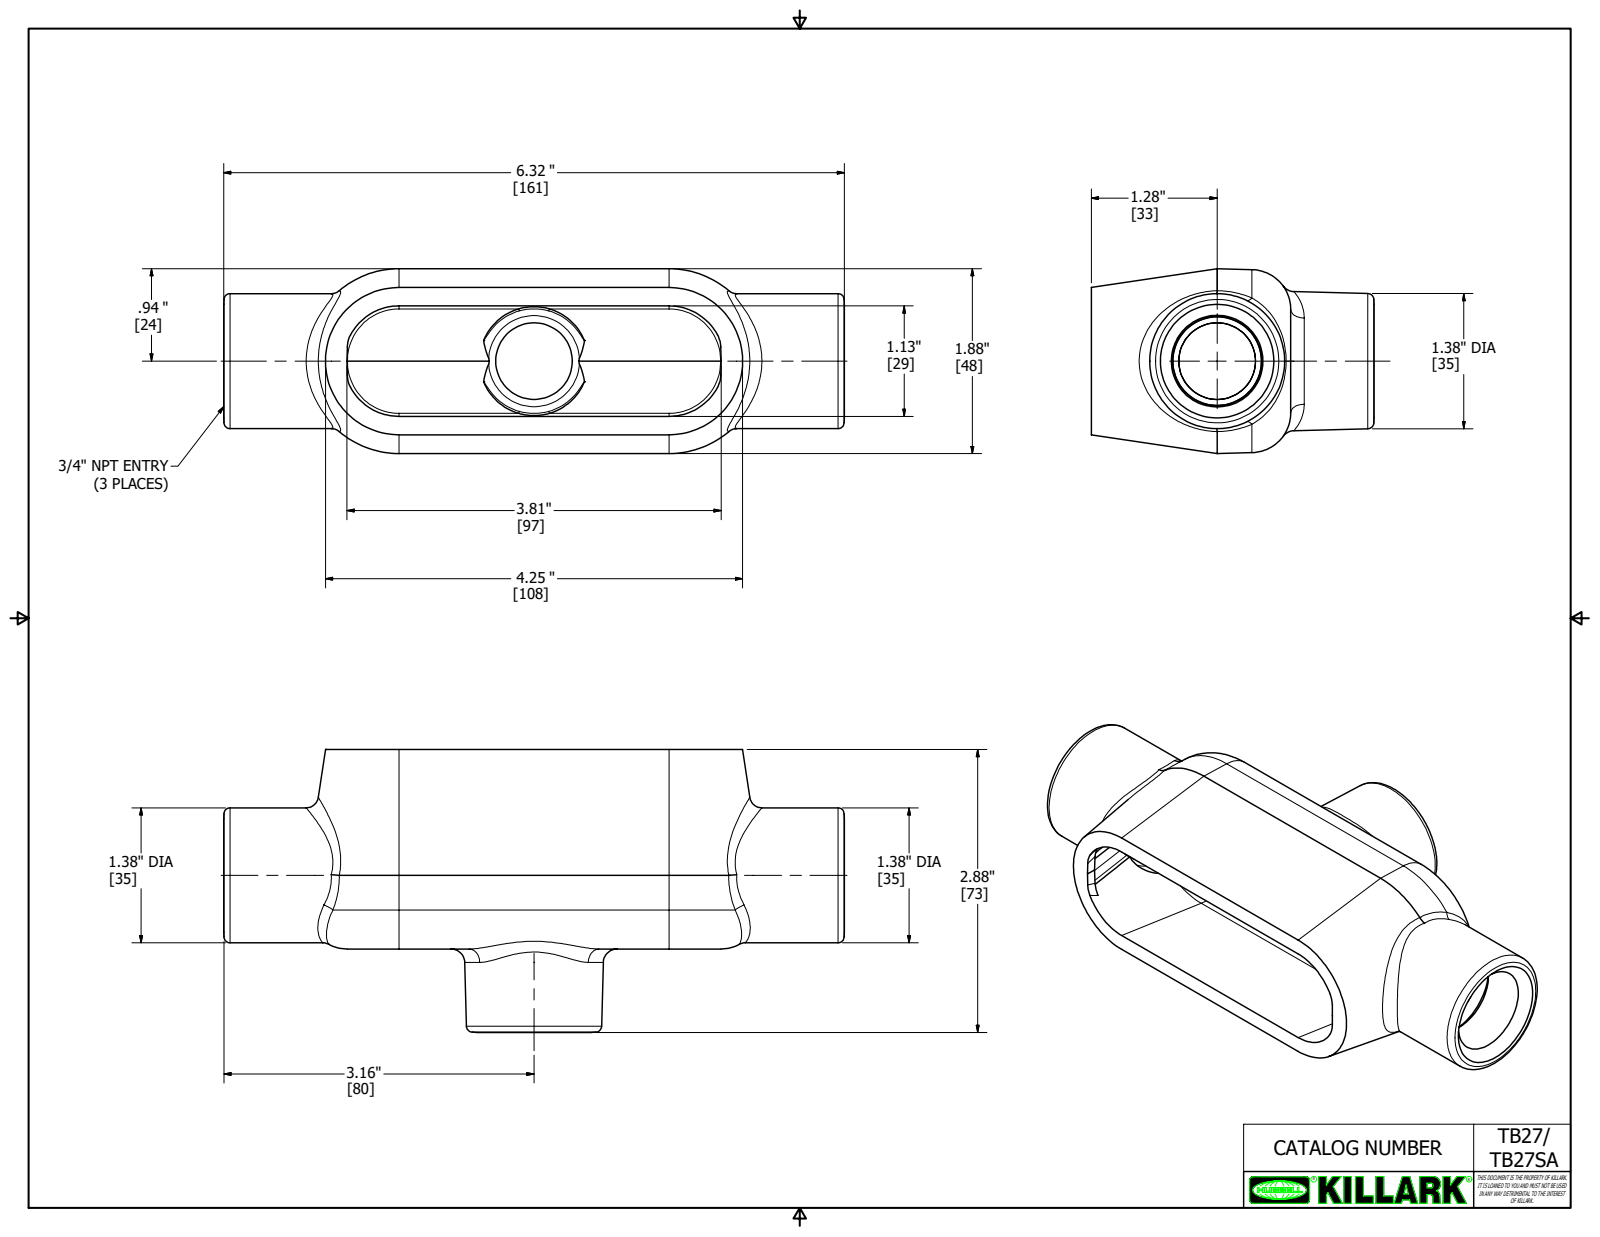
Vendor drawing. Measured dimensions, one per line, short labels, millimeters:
name: 17661-2
written by: Autodesk Inventor 2018 (AUTOMOTIVE_DESIGN)
unit: mm
bodies: 1 solid, 891 faces (515 planar, 43 cylindrical, 333 other)
size: 160.6 × 73.2 × 47.8
volume: 107 400 mm³; area: 47 050 mm²
holes: 2× ⌀26.8, 1× ⌀1.2, 1× ⌀10.3, 1× ⌀28.2
bosses: 1× ⌀34.9, 1× ⌀12.7, 1× ⌀1.4
rounds: 10× R1.6, 2× R1.6, 2× R5.6, 2× R10.3, 2× R12.7, 1× R0.2, 1× R0.2, 1× R0.4
face distances: 4.7, 51.6, 4.7, 0.8, 50.8, 0.8, 5.5, 44, 10.7, 6.4
hole spacings: 3.1
